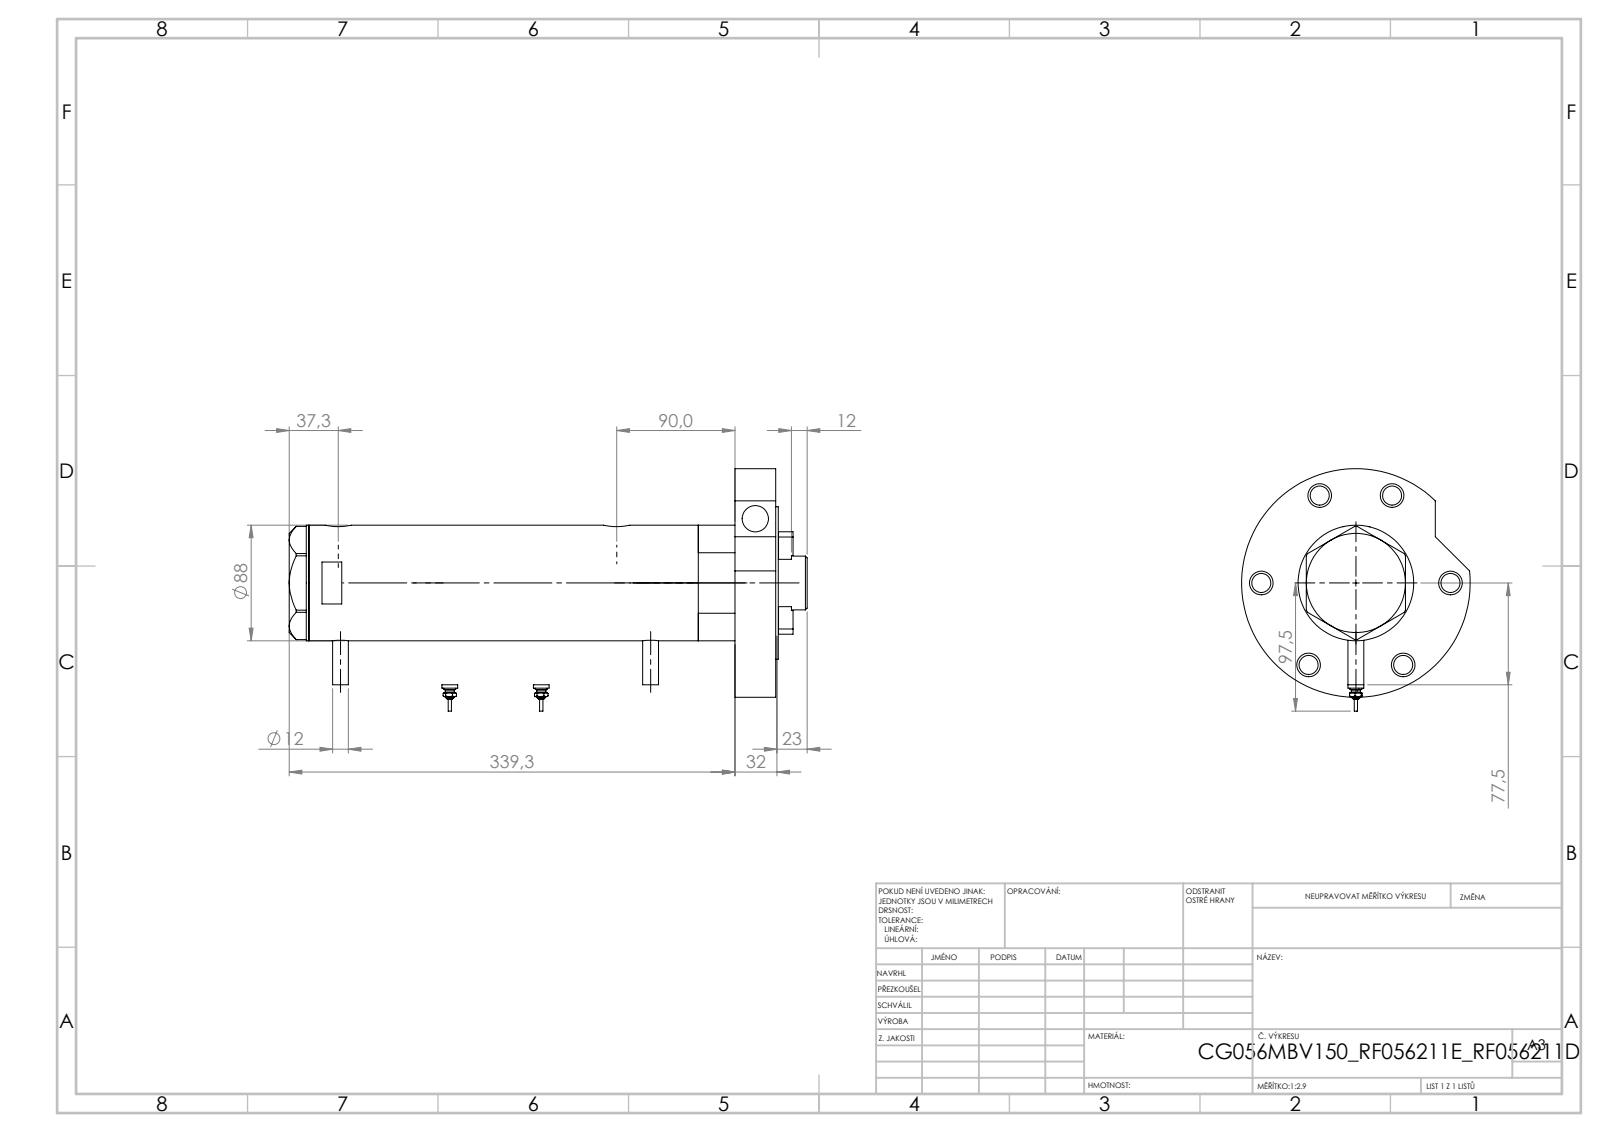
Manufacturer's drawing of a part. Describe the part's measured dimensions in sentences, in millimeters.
The part is named "V270CG_BACK; V270CG_MIDDLE; V270CG_RF211D; V270CG_RF211E (+3 more)". Its 3-D file was written by "SolidWorks 2019 (CONFIG_CONTROL_DESIGN)". It is 9 solids with 297 faces: 115 planar, 118 cylindrical and 64 other. Overall it measures 394.3 by 184.5 by 174 millimeters. Its volume is 2 572 000 cubic millimeters and its surface area 367 326 square millimeters. Round holes: 7 of diameter 14.5, 6 of diameter 18, 4 of diameter 8.1, 4 of diameter 13.5, 3 of diameter 20, 2 of diameter 12.5, 2 of diameter 13.16, 1 of diameter 42, 1 of diameter 43.5, 1 of diameter 56, 1 of diameter 60, 1 of diameter 75. Round bosses or shafts: 4 of diameter 12, 2 of diameter 9, 2 of diameter 7, 2 of diameter 4.5, 2 of diameter 2.5, 1 of diameter 174, 1 of diameter 116, 1 of diameter 88. The main face-to-face distances are 31, 357.3, 2, 324.3, 355.3, 33, 234.4, 89.9, 120.9, 122.9. The hole center spacings are 72, 30.35, 69.35, 86.03, 18, 41.87, 42.93, 52.39.
